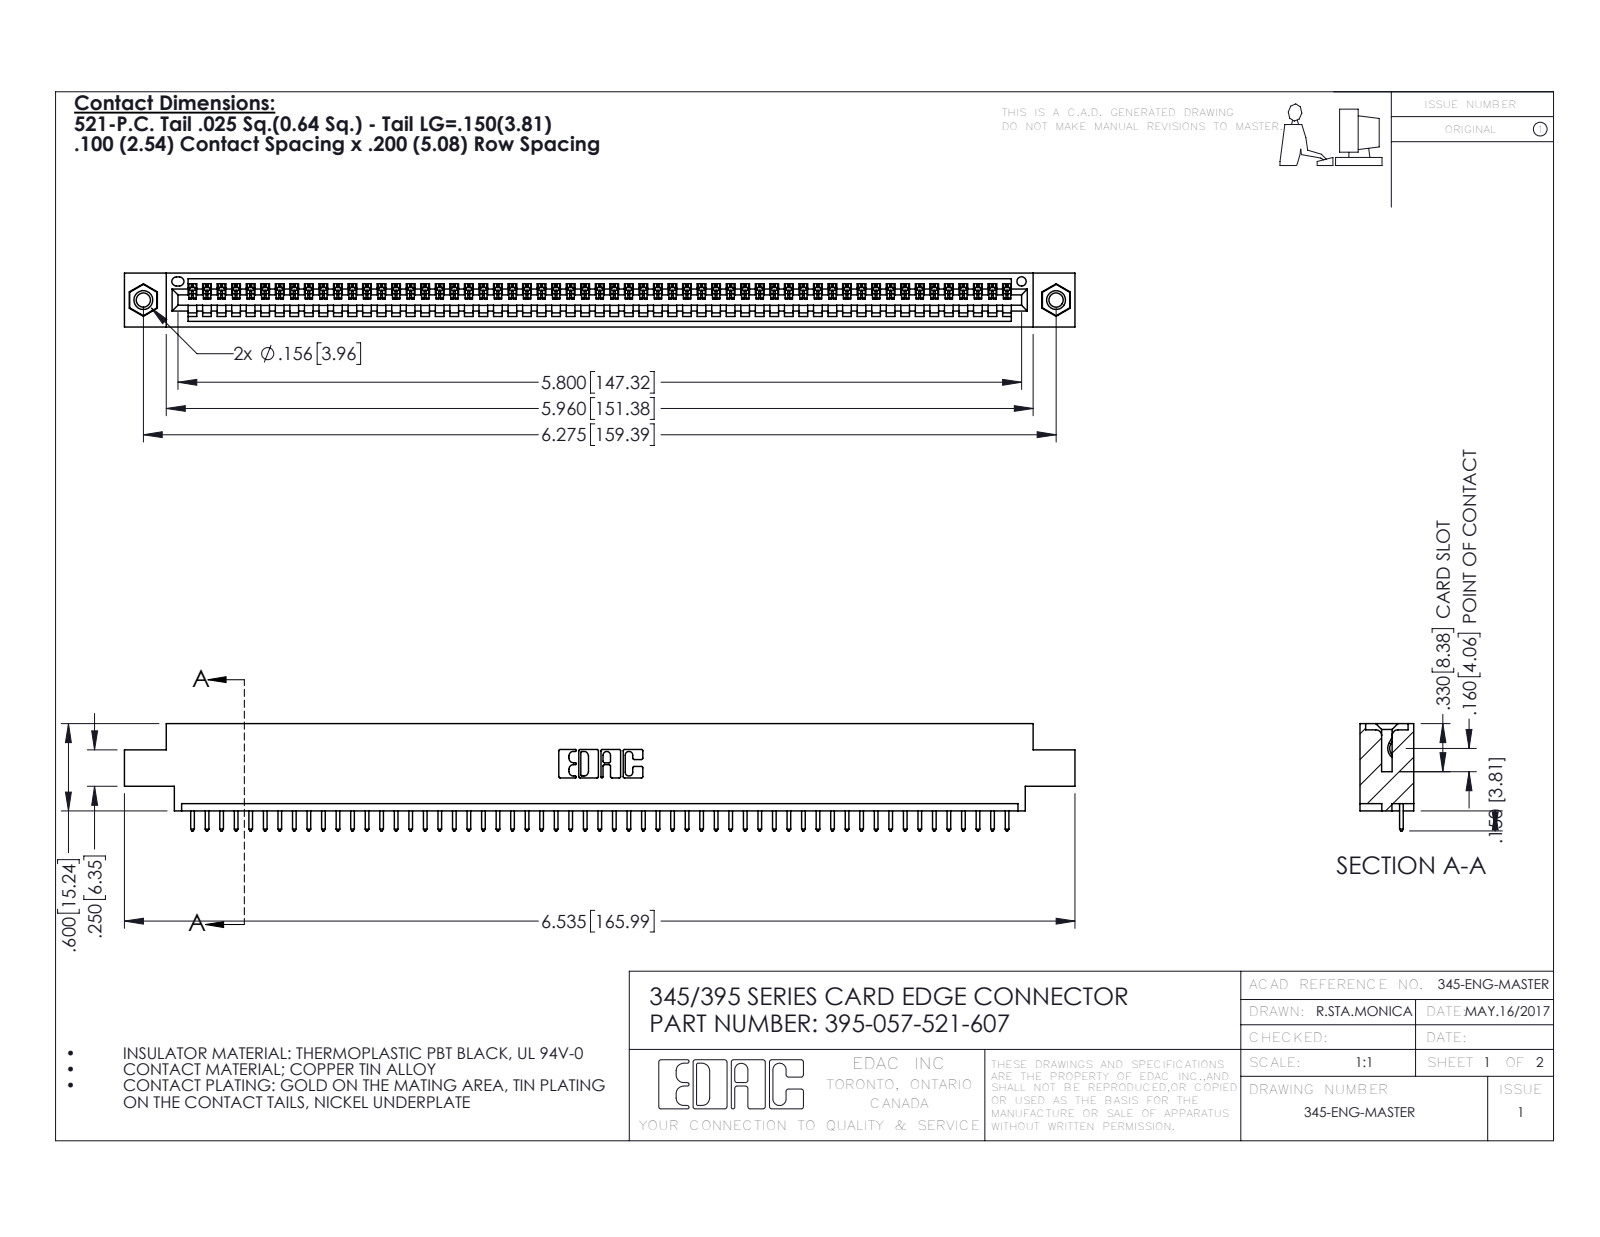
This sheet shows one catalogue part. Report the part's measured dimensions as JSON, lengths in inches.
{"part_name": "345-250-001_345-250-005-103; 345 Part_0.170 Offset - 0.156 Dia-TI; 345-292-001_345-293-121; 395-057-521-607", "step_written_by": "SolidWorks 2016 (CONFIG_CONTROL_DESIGN)", "units": "inches", "bodies": {"solids": 60, "faces": 3496, "planar": 2396, "cylindrical": 1084, "other": 16}, "overall_size": [6.535, 0.737, 0.37], "volume_in3": 0.952, "surface_area_in2": 31.71, "round_holes": [[0.098, 2], [0.125, 2], [0.156, 2], [0.064, 1]], "round_bosses_or_shafts": [[0.155, 2]], "partial_cylinders_radius": [[0.006, 114], [0.01, 114], [0.01, 22], [0.007, 6], [0.031, 6], [0.026, 3], [0.031, 2], [0.04, 2]], "face_to_face_distances": [0.072, 0.298, 0.37, 0.2, 0.098, 0.272, 0.025, 0.225, 0.175, 0.149], "hole_center_spacings": [0.27, 6.039, 6.275]}
